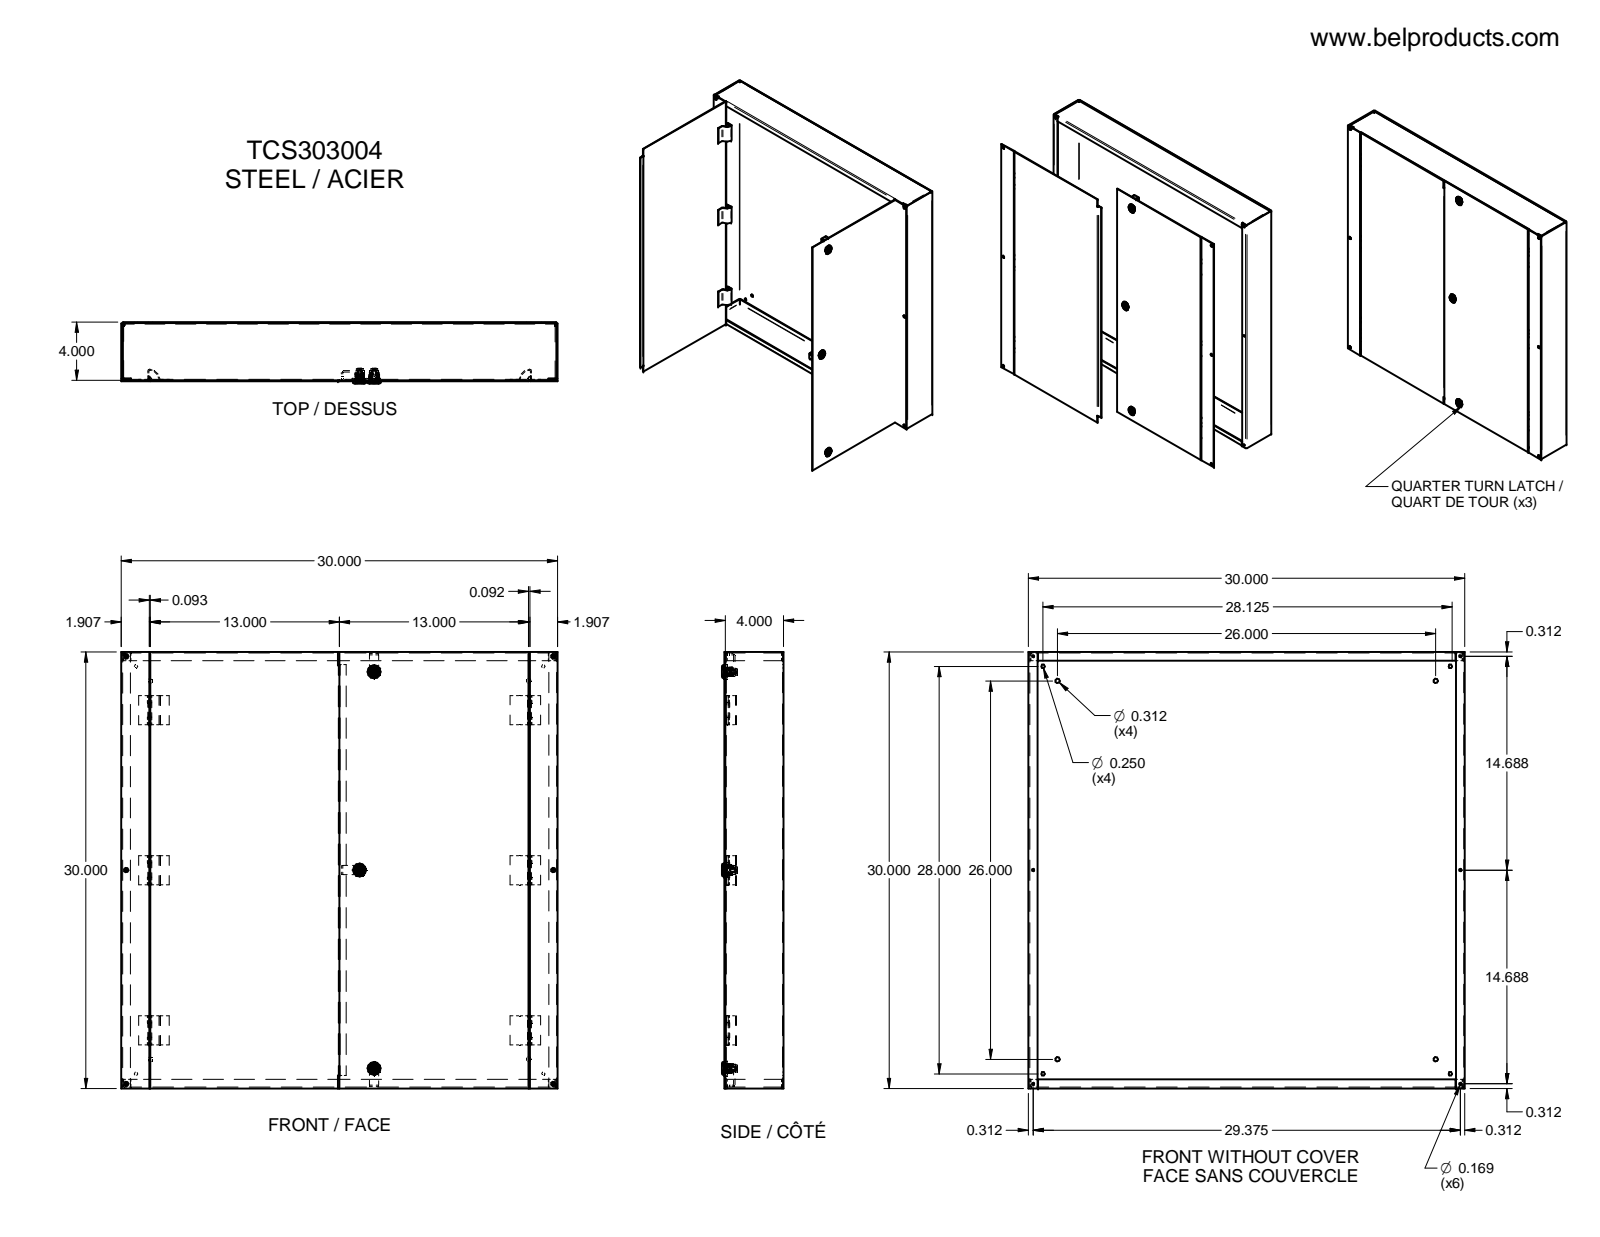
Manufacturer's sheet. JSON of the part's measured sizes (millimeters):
{"part_name": "LOCK AVEC TOURNEVIS TYPE 4-12 SANS CAME; HOSING-oa0; INSERT POUR TOURNEVIS-oa1; NOIX DE FIXATION-oa2 (+8 more)", "step_written_by": "Unknown (AUTOMOTIVE_DESIGN)", "units": "millimeters", "bodies": {"solids": 46, "faces": 1689, "planar": 850, "cylindrical": 417, "other": 422}, "overall_size": [762, 762, 107.97], "volume_mm3": 2984000, "surface_area_mm2": 3177000, "round_holes": [[7.92, 10], [4.29, 6], [6.35, 4], [9.1, 3], [11.18, 3], [12.83, 3], [15.8, 3], [17.46, 3], [3.81, 2], [6.99, 2]], "round_bosses_or_shafts": [[22.86, 3], [22.61, 3], [15.75, 3], [12.95, 3], [12.62, 3], [12.19, 3], [11.86, 3], [10.08, 3]], "partial_cylinders_radius": [[9.53, 34], [0.25, 24], [0.81, 17], [2.72, 14], [9.42, 6], [1.52, 4], [3.05, 4], [3.48, 3]], "face_to_face_distances": [1.91, 101.6, 99.69, 103.51, 1.9, 760.1, 762, 758.2, 101.59, 103.5], "hole_center_spacings": [686.27, 704.56, 728.87, 746.12, 24.69, 35.92, 60.61, 332.97]}
